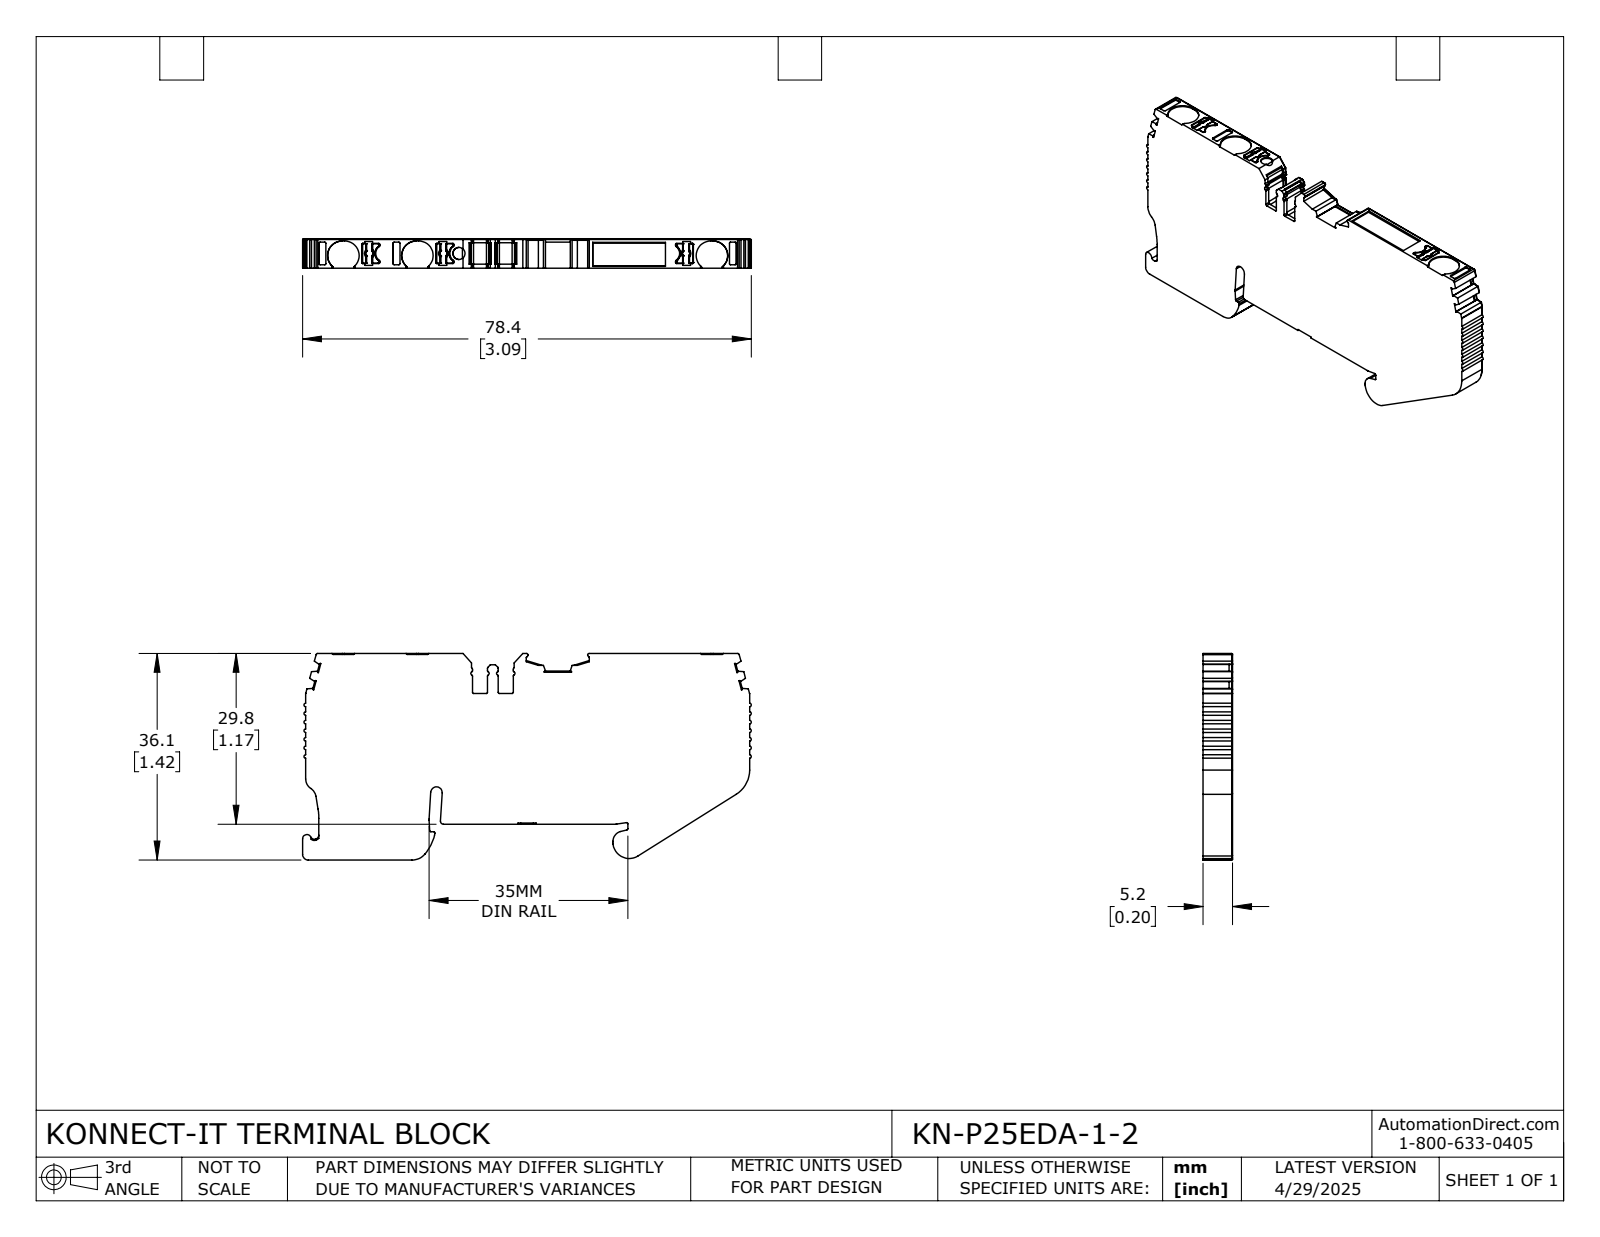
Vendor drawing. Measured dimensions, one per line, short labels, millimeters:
name: KN-P25EDA-1-2
written by: SolidWorks 2024 (CONFIG_CONTROL_DESIGN)
unit: mm
bodies: 1 solid, 665 faces (349 planar, 265 cylindrical, 51 other)
size: 78.36 × 36.07 × 5.15
volume: 11 968 mm³; area: 6 211 mm²
holes: 1× ⌀2.1
rounds: 66× R0.2, 39× R0.3, 19× R0.1, 18× R0.5, 12× R0.15, 9× R0.4, 6× R2.55, 3× R1
face distances: 5.15, 29.61, 29.81, 6.26, 35.87, 36.07, 77.52, 1.2, 5, 4.5
